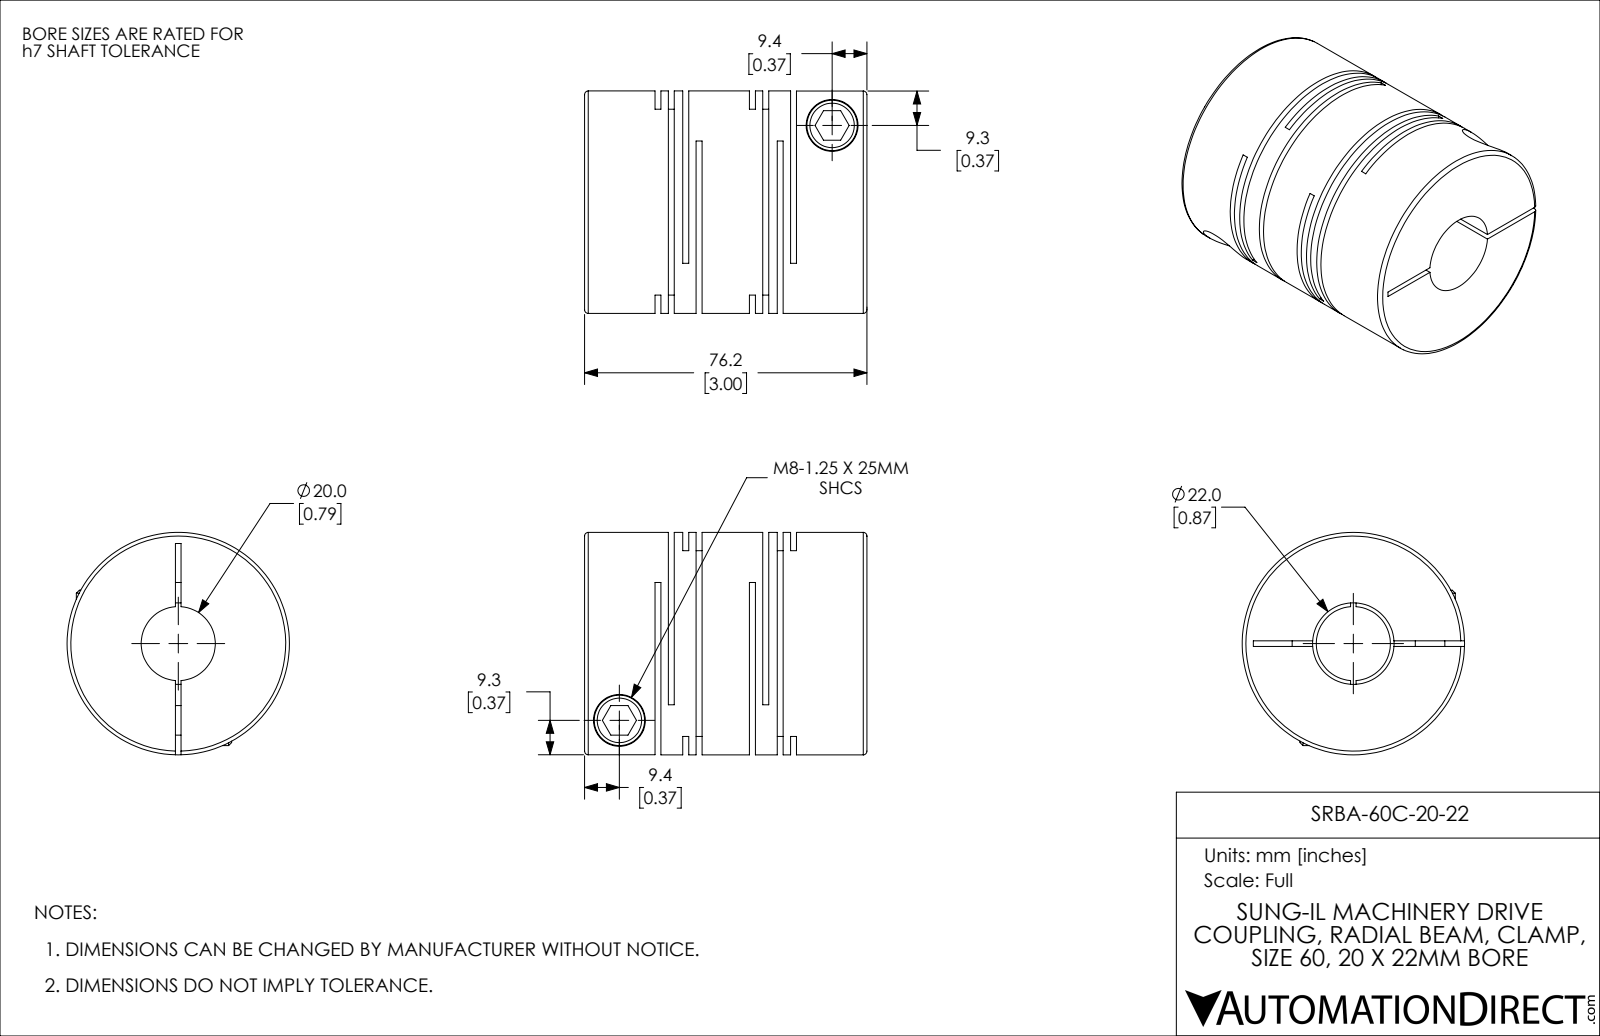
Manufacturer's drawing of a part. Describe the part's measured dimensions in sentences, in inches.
The part is named "SRBA-60C-20-22". Its 3-D file was written by "SolidWorks 2021 (CONFIG_CONTROL_DESIGN)". It is 1 solid with 115 faces: 60 planar, 42 cylindrical and 13 other. Overall it measures 3 by 2.362 by 2.362 inches. Its volume is 9.606 cubic inches and its surface area 90.33 square inches. Round holes: 2 of diameter 0.315, 2 of diameter 0.551, 1 of diameter 0.787, 1 of diameter 0.866. Round bosses or shafts: 2 of diameter 0.535, 1 of diameter 2.362. The main face-to-face distances are 0.063, 0.142, 0.295, 1.004, 1.299, 1.067, 0.709, 0.079, 0.232, 0.941.
